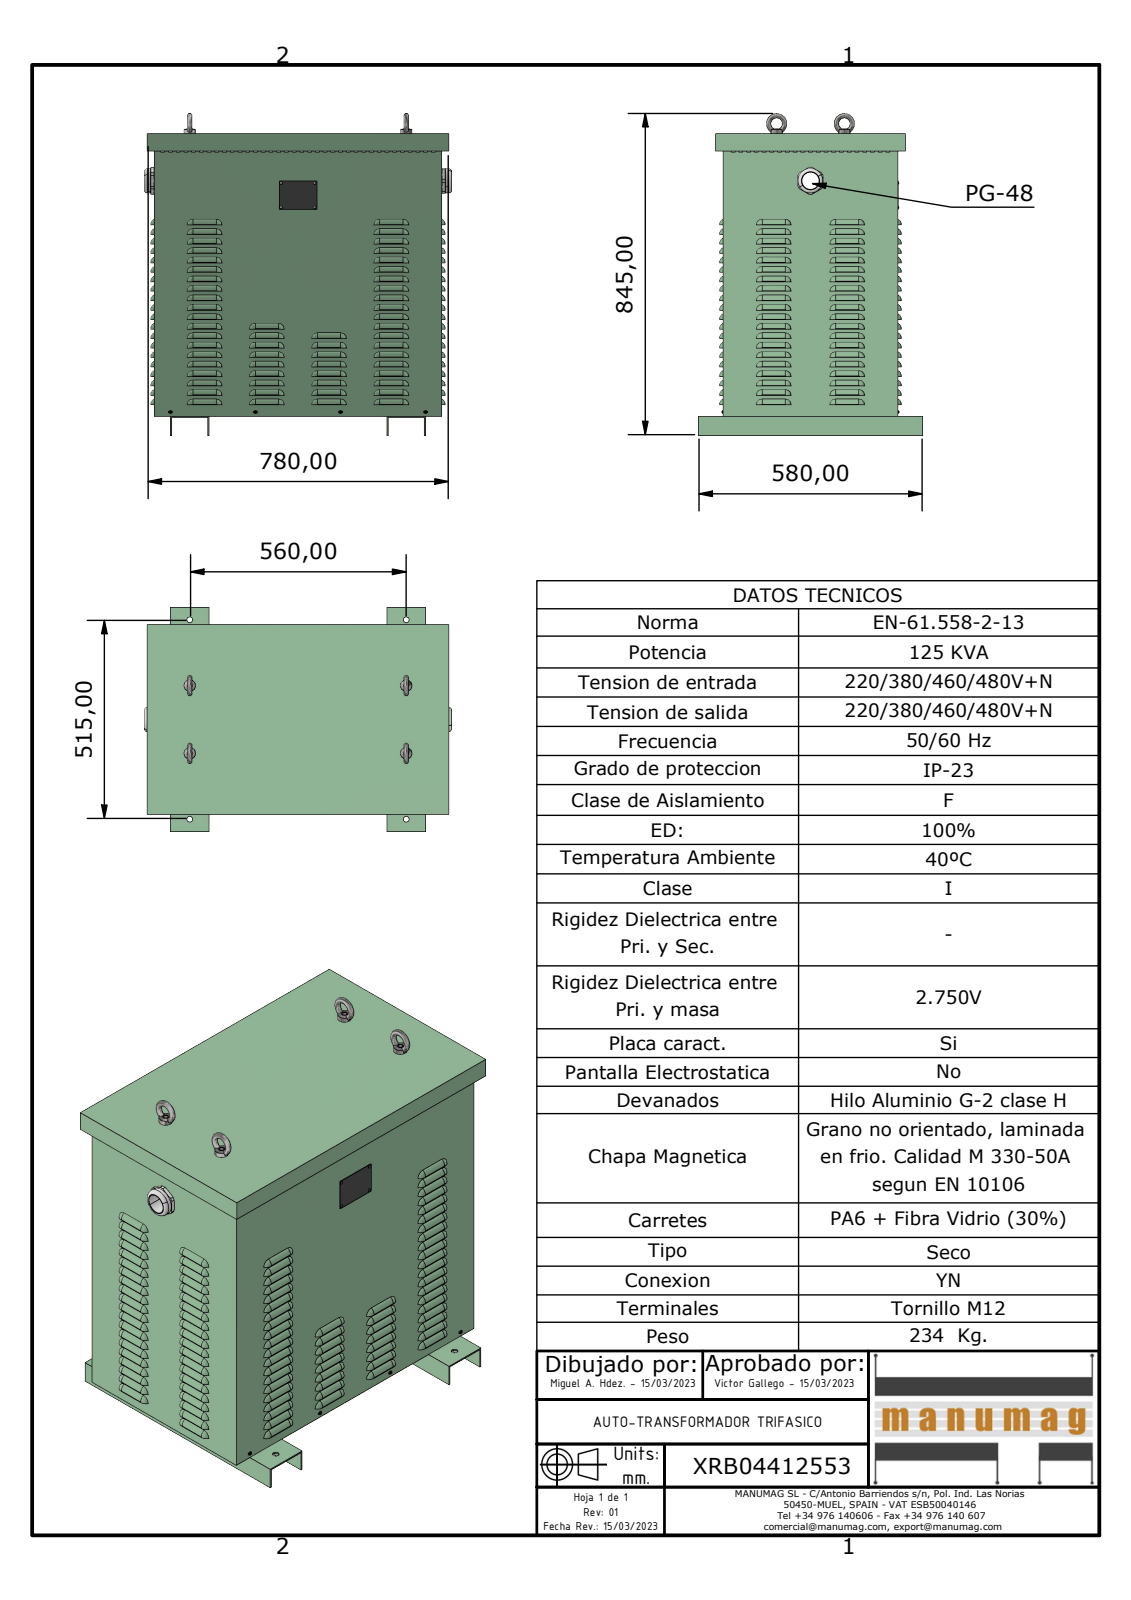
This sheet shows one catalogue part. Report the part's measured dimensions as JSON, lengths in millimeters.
{"part_name": "XRB04412553; JE125 - JE160NACIONAL CUERPO; JE125 JE160 NACIONAL BASE; JE125 - JE160 NACIONAL PATA (+6 more)", "step_written_by": "Autodesk Inventor 2023 (AUTOMOTIVE_DESIGN)", "units": "millimeters", "bodies": {"solids": 24, "faces": 4123, "planar": 1445, "cylindrical": 1686, "other": 992}, "overall_size": [835, 795.27, 580], "volume_mm3": 6672000, "surface_area_mm2": 5912000, "round_holes": [[11, 780], [15, 8], [4, 4], [5, 4], [10.11, 4], [44, 1], [60, 1]], "round_bosses_or_shafts": [[30, 4], [4, 4], [3.62, 4], [3.2, 4], [63, 1], [59.3, 1], [59.15, 1], [57.63, 1]], "partial_cylinders_radius": [[14, 194], [7, 80], [15, 80], [2.5, 8], [2, 4], [35, 1]], "face_to_face_distances": [2, 450, 730, 742, 448, 452, 732, 740, 728, 744], "hole_center_spacings": [20.79, 164.63, 33.28, 149.69, 179, 30, 47.25, 149]}
